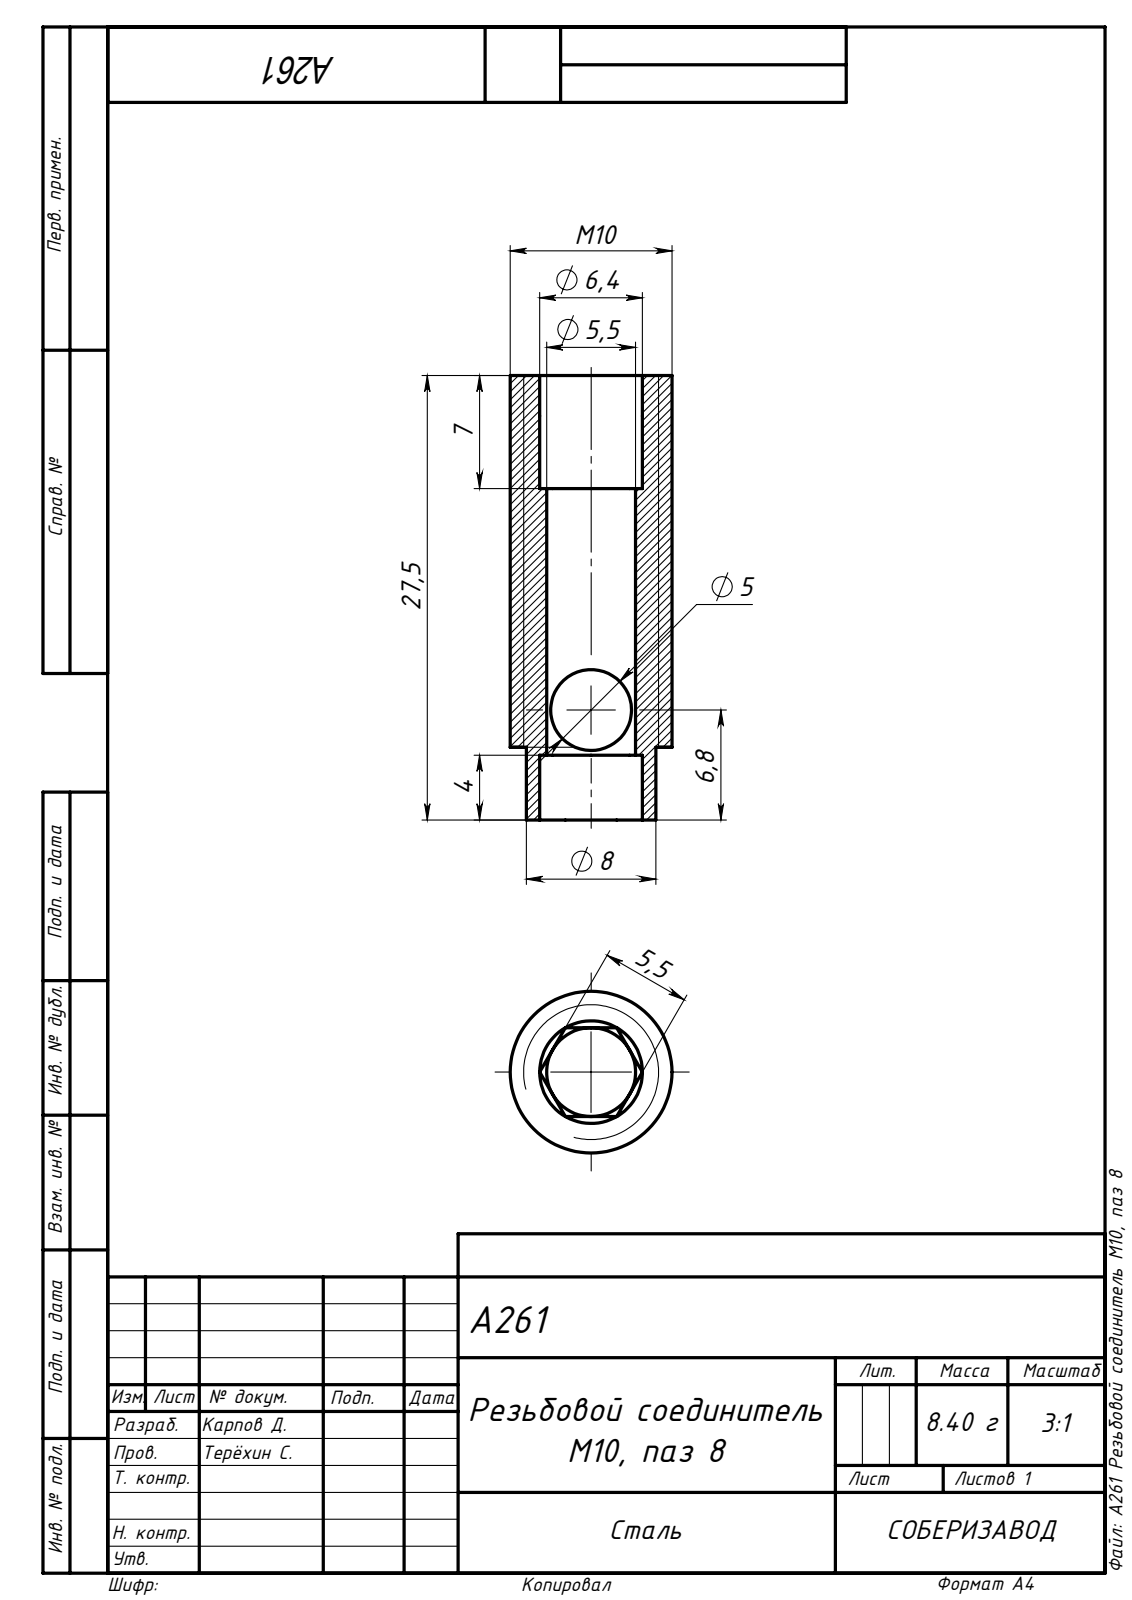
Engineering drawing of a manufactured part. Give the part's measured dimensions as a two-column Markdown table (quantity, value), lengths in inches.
| quantity | value |
| --- | --- |
| part name | A261 Резьбовой соединитель M10, паз 8 |
| STEP written by | SolidWorks 2021 (AUTOMOTIVE_DESIGN) |
| units | inches |
| bodies | 1 solid, 46 faces (34 planar, 12 cylindrical, 0 other) |
| overall size | 1.083 × 0.394 × 0.394 |
| volume | 0.076 in³ |
| surface area | 2.218 in² |
| round holes (diameter × count) | 0.197 × 1, 0.217 × 1, 0.25 × 1 |
| round bosses / shafts (diameter × count) | 0.394 × 1, 0.315 × 1 |
| main face-to-face distances | 0.217, 0.177, 0.906, 1.083, 0.807, 0.098, 0.984, 0.925, 0.827, 0.02 |
